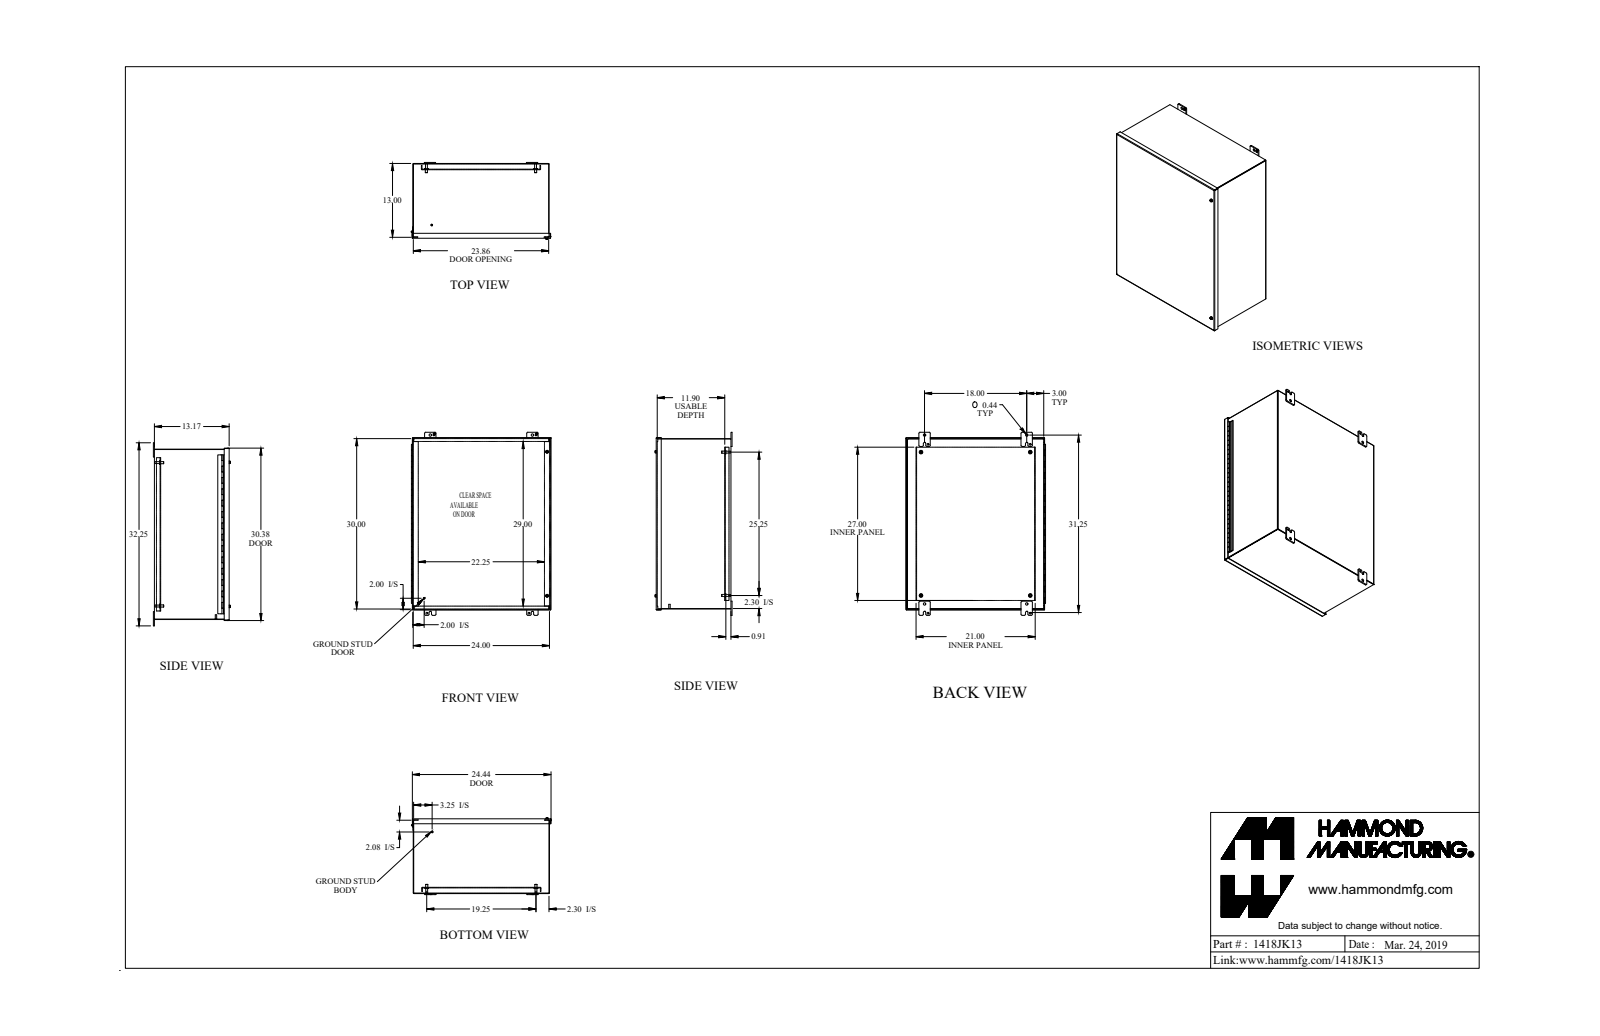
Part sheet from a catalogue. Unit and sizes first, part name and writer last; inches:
Units: inches
Overall size (bounding box): 32.25 × 24.604 × 13.571
Round holes (diameter × count): ⌀0.313 ×6, ⌀0.437 ×4, ⌀0.5 ×4, ⌀0.26 ×2, ⌀0.266 ×2, ⌀0.28 ×2, ⌀0.29 ×2, ⌀0.307 ×2, ⌀0.397 ×2, ⌀0.445 ×2, ⌀0.187 ×1, ⌀3.5 ×1
Round bosses / shafts (diameter × count): ⌀0.65 ×4, ⌀0.375 ×4, ⌀0.33 ×4, ⌀1 ×2, ⌀0.51 ×2, ⌀0.5 ×2, ⌀0.39 ×2, ⌀0.281 ×2
Partial cylindrical surfaces — rounded edges, fillets, slot ends (radius × count): R0.188 ×24, R0.25 ×20, R0.036 ×10, R0.108 ×10, R0.218 ×8, R0.133 ×6, R0.06 ×5, R0.125 ×4
Main face-to-face distances: 0.072, 13.1, 23.928, 13.172, 13.028, 29.93, 0.095, 1.104, 1.032, 11.996
Hole centre spacings: 1.735, 18, 25.25, 29.75, 31.751, 34.772, 3.065, 26.757
Volume: 310.2 in³ · Surface area: 7 802 in²
Bodies: 34 solids, 966 faces (591 planar, 333 cylindrical, 42 other)
Part name (STEP PRODUCT): 1418JK13_Default
STEP written by: SolidWorks 2018 (CONFIG_CONTROL_DESIGN)
